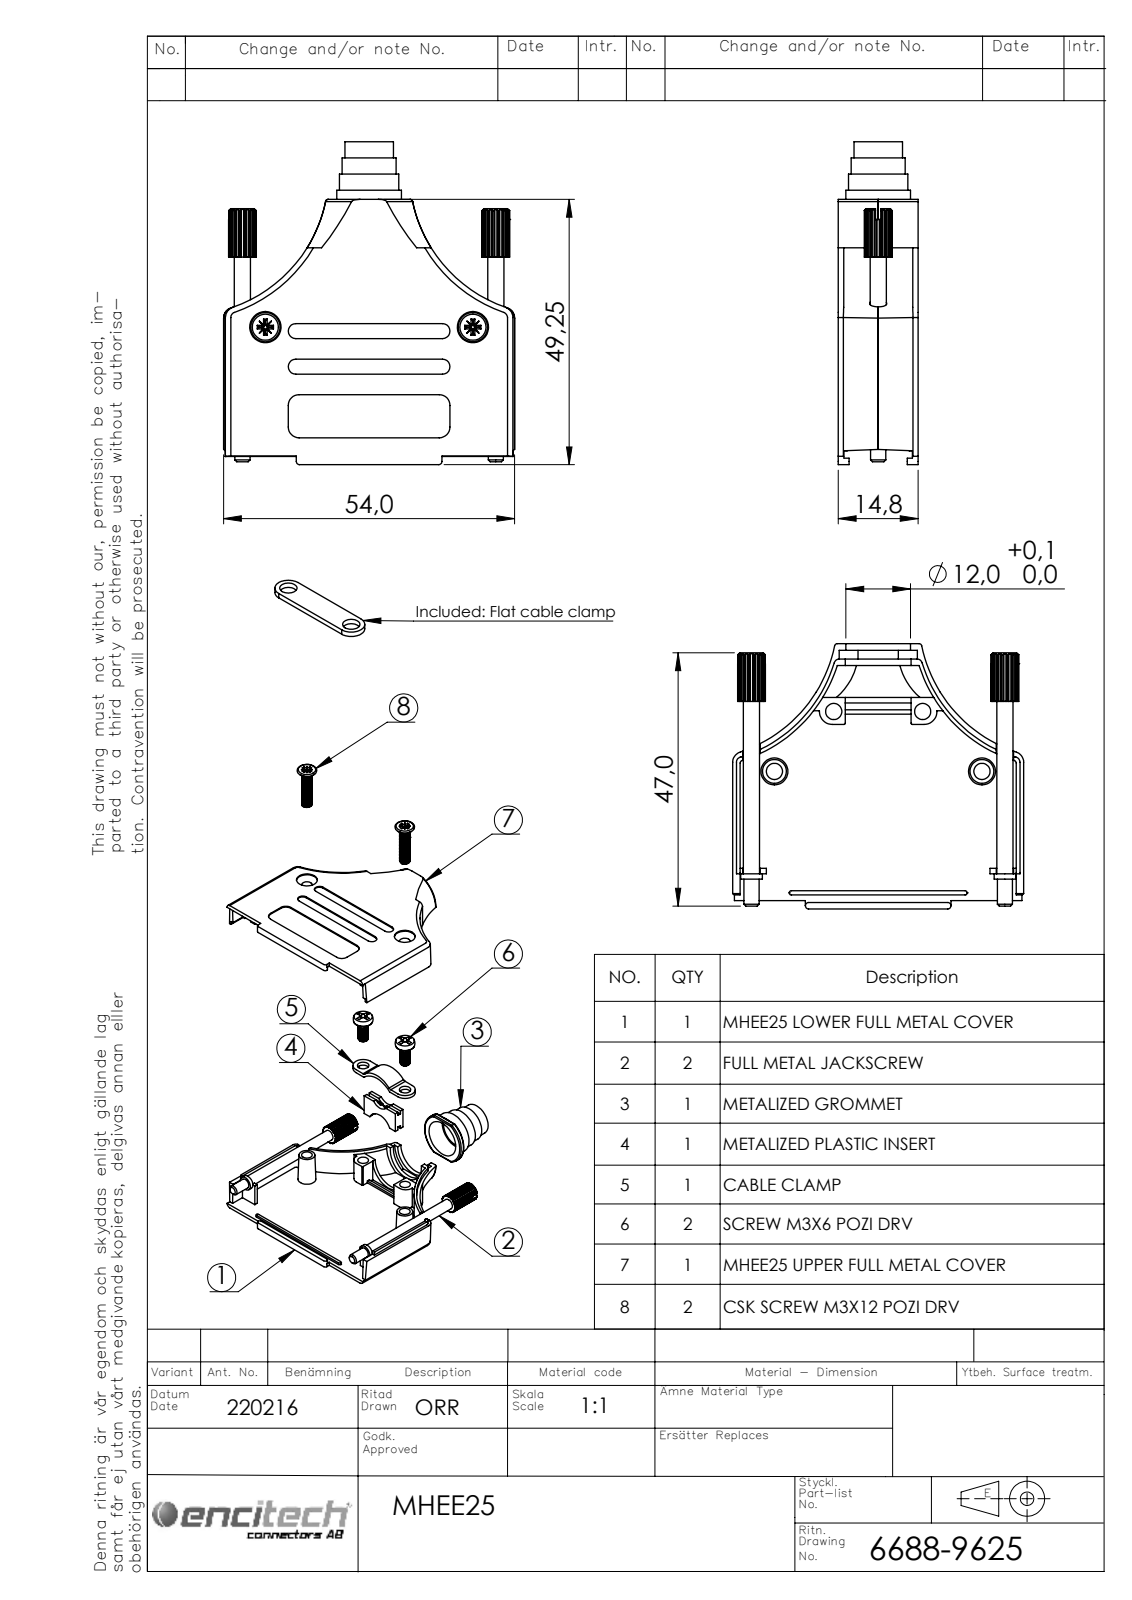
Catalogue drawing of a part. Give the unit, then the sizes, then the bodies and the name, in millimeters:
Units: millimetres
Overall size (bounding box): 59.95 × 54 × 14.8
Round holes (diameter × count): ⌀3 ×4, ⌀3.2 ×4, ⌀4.5 ×2, ⌀5.8 ×2, ⌀7.5 ×1, ⌀8.5 ×1, ⌀9.5 ×1, ⌀10.5 ×1, ⌀12 ×1, ⌀12.2 ×1
Round bosses / shafts (diameter × count): ⌀2.9 ×4, ⌀5 ×2, ⌀4 ×2, ⌀3 ×2, ⌀2.8 ×2, ⌀11 ×1, ⌀10 ×1, ⌀9 ×1
Partial cylindrical surfaces — rounded edges, fillets, slot ends (radius × count): R1 ×14, R26.4 ×10, R0.1 ×8, R0.2 ×4, R0.3 ×4, R1.4 ×4, R2 ×4, R0.25 ×3
Main face-to-face distances: 13.75, 1.05, 12.7, 14.8, 0.75, 14.5, 13.45, 6.35, 7.1, 7.4
Hole centre spacings: 15.64, 23.5, 29.66, 16.5, 38.5, 47
Volume: 8 455 mm³ · Surface area: 16 587 mm²
Bodies: 11 solids, 879 faces (424 planar, 351 cylindrical, 104 other)
Part name (STEP PRODUCT): 6855-0117-13; 6805-0136-03; Cone MHEE; 6826-0141-02 (+5 more)
STEP written by: SolidWorks 2021 (AUTOMOTIVE_DESIGN)
